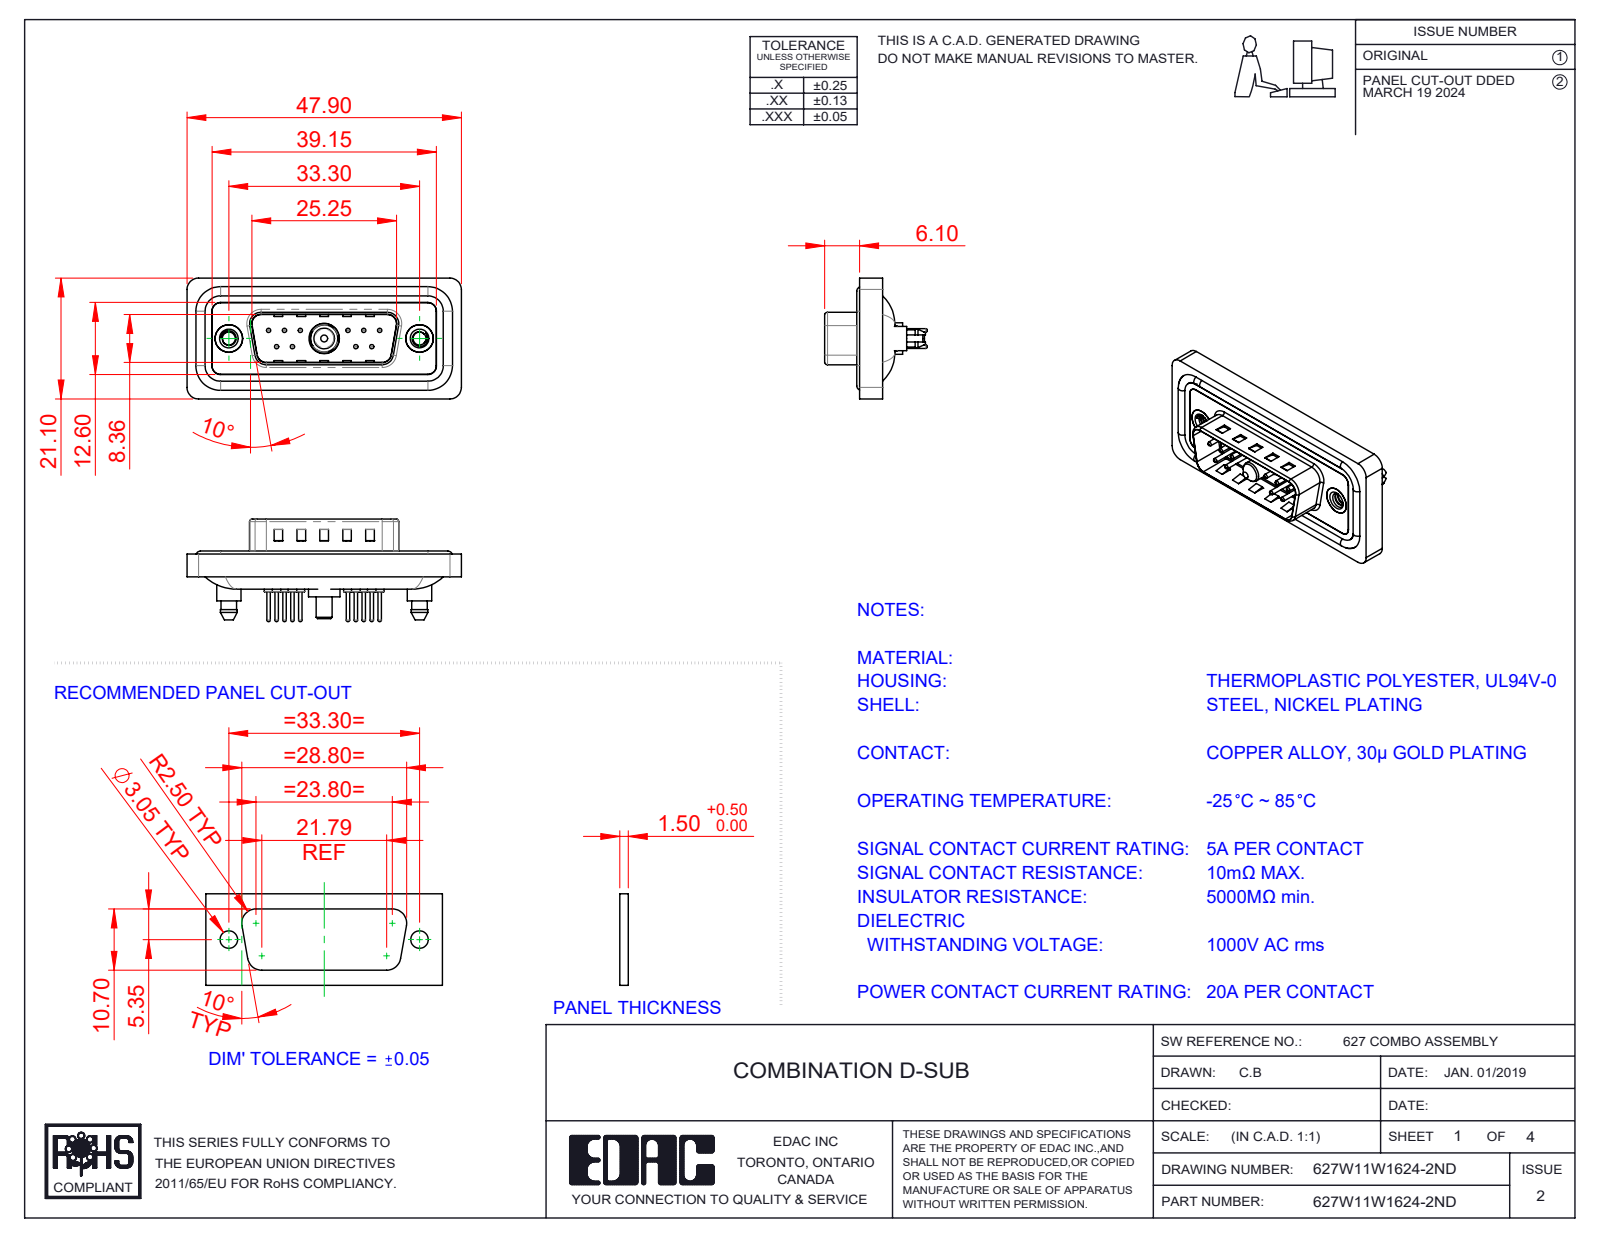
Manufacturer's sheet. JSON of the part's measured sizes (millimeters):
{"part_name": "627Combo Housing_11W1; 627W11W1624-2ND; 627Combo Shell Rear_15 Contacts; 627Combo Shell Front_15 Contacts (+6 more)", "step_written_by": "SolidWorks 2023 (CONFIG_CONTROL_DESIGN)", "units": "millimeters", "bodies": {"solids": 19, "faces": 927, "planar": 282, "cylindrical": 387, "other": 258}, "overall_size": [47.9, 21.1, 17.9], "volume_mm3": 5582, "surface_area_mm2": 9172, "round_holes": [[0.75, 10], [1.6, 10], [2, 10], [2.26, 2], [4, 2], [4.8, 2], [5, 2], [4.85, 1], [5.3, 1]], "round_bosses_or_shafts": [[1.5, 10], [0.6, 10], [1.6, 4], [5.4, 2], [4.9, 2], [4.25, 2], [5.5, 1], [5.2, 1]], "partial_cylinders_radius": [[1.5, 28], [2, 20], [1.6, 10], [0.5, 8], [1, 7], [0.25, 4], [0.6, 4], [0.65, 4]], "face_to_face_distances": [0.4, 1.1, 1.6, 1.5, 2.9, 0.5, 3.1, 4.1, 0.82, 9.58], "hole_center_spacings": [3.16, 2.77, 13.85, 11.08, 16.62, 5.03, 5.04, 5.54]}
